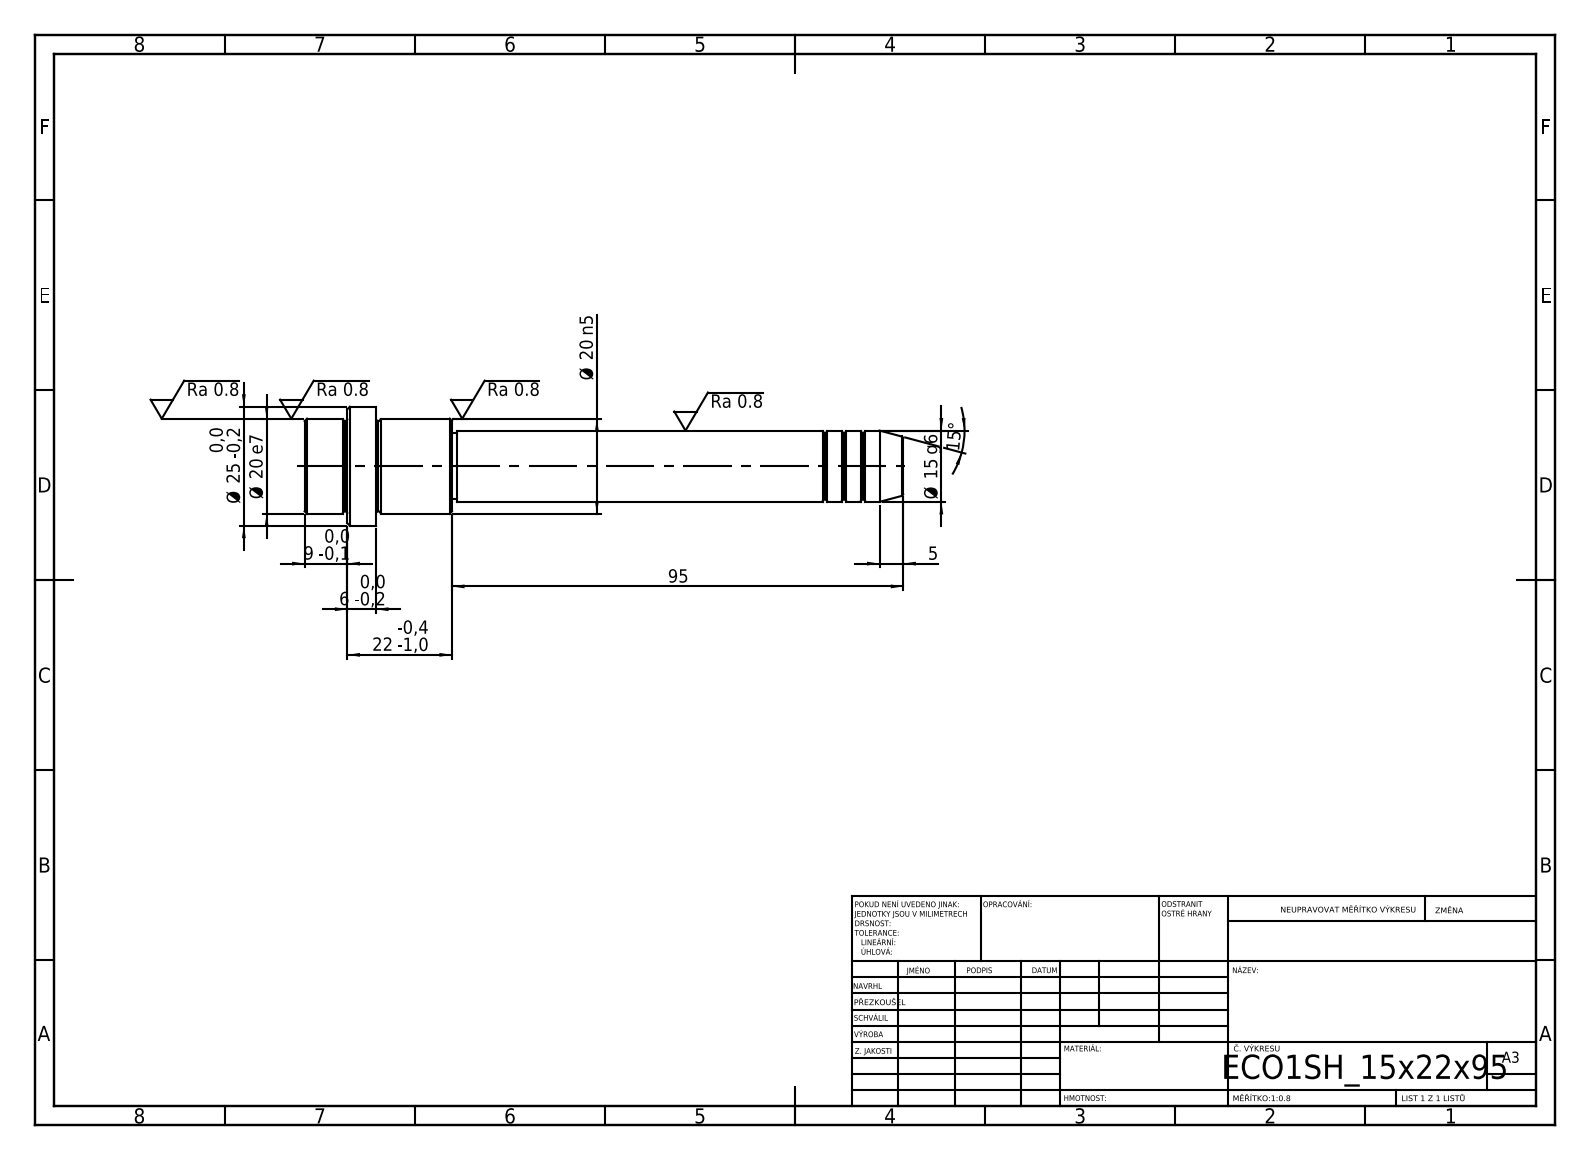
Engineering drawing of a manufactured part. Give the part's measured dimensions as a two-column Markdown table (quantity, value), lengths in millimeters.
| quantity | value |
| --- | --- |
| STEP written by | SolidWorks 2019 (CONFIG_CONTROL_DESIGN) |
| units | millimeters |
| bodies | 1 solid, 52 faces (6 planar, 16 cylindrical, 30 other) |
| overall size | 126 × 25 × 25 |
| volume | 27 287 mm³ |
| surface area | 7 543 mm² |
| round bosses / shafts (diameter × count) | 25 × 1, 20 × 1, 15 × 1, 14 × 1 |
| main face-to-face distances | 15, 6, 9, 16, 22, 31, 95, 111, 117, 126 |
